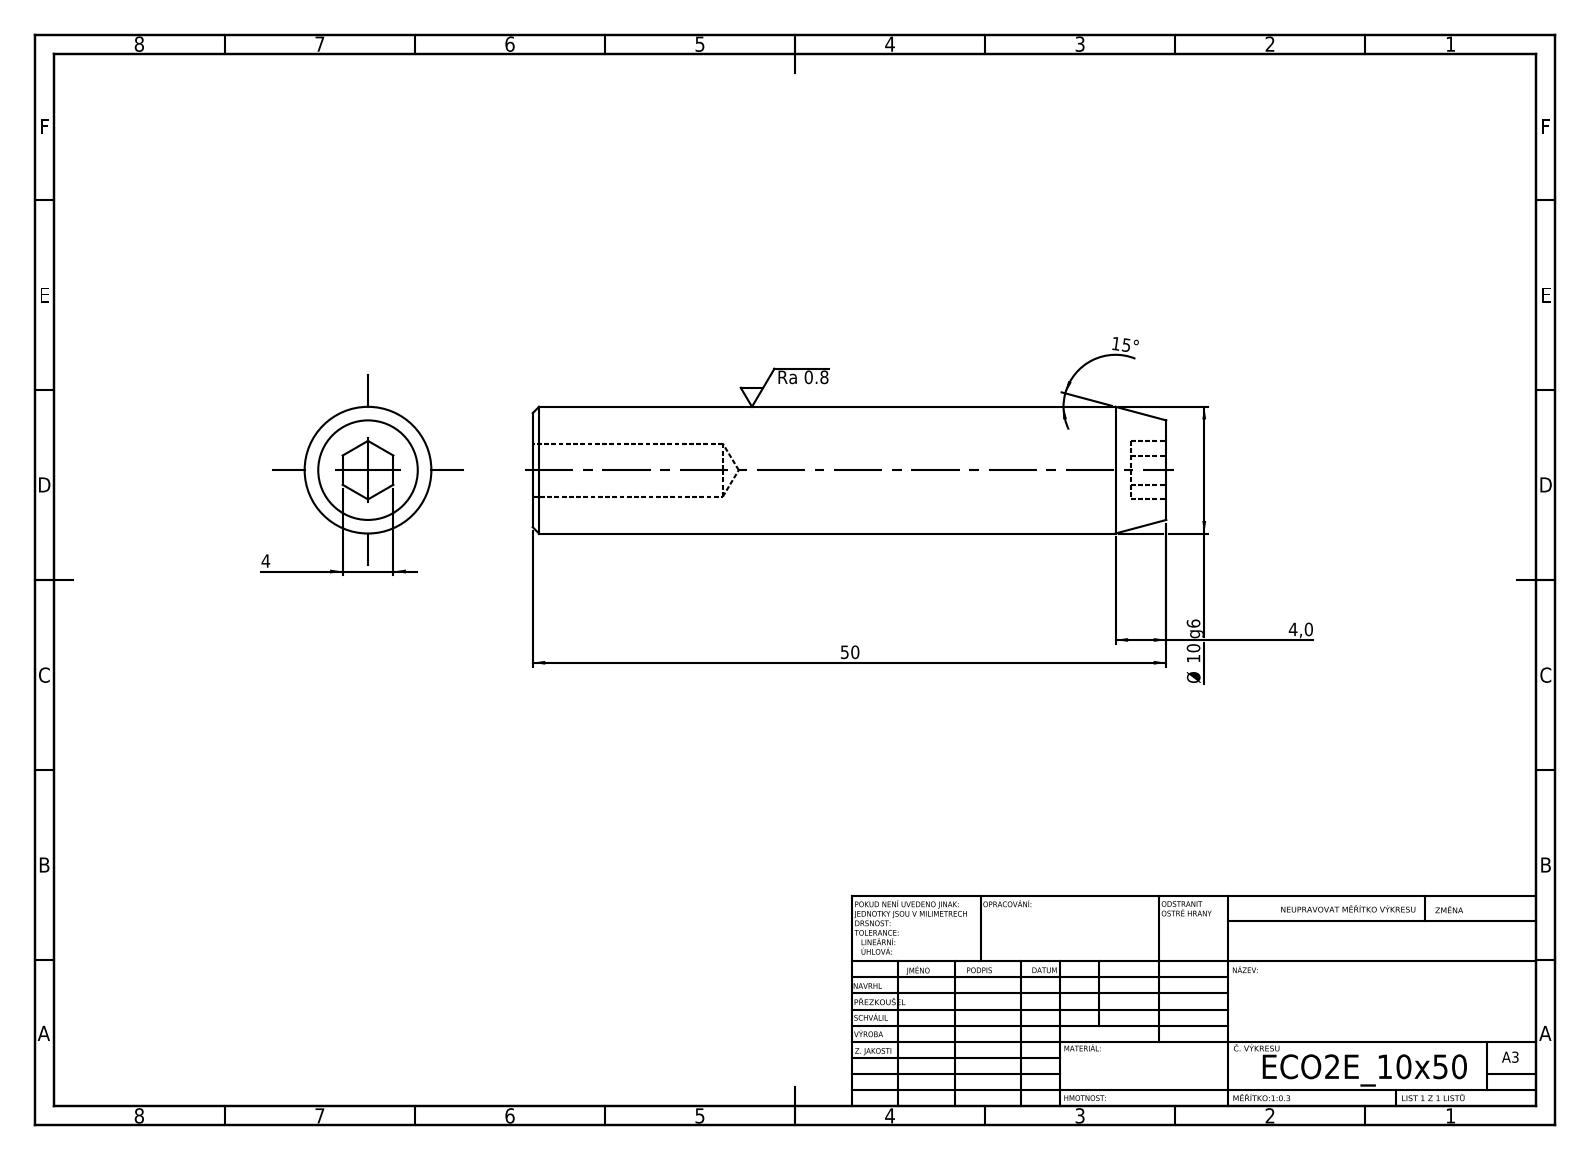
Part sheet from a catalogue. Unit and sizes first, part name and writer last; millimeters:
Units: millimetres
Overall size (bounding box): 50 × 10 × 10
Round holes (diameter × count): ⌀4.2 ×1
Round bosses / shafts (diameter × count): ⌀10 ×1
Main face-to-face distances: 50, 4, 2.8, 47.2
Volume: 3 608 mm³ · Surface area: 1 918 mm²
Bodies: 1 solid, 19 faces (9 planar, 4 cylindrical, 6 other)
STEP written by: SolidWorks 2019 (CONFIG_CONTROL_DESIGN)
